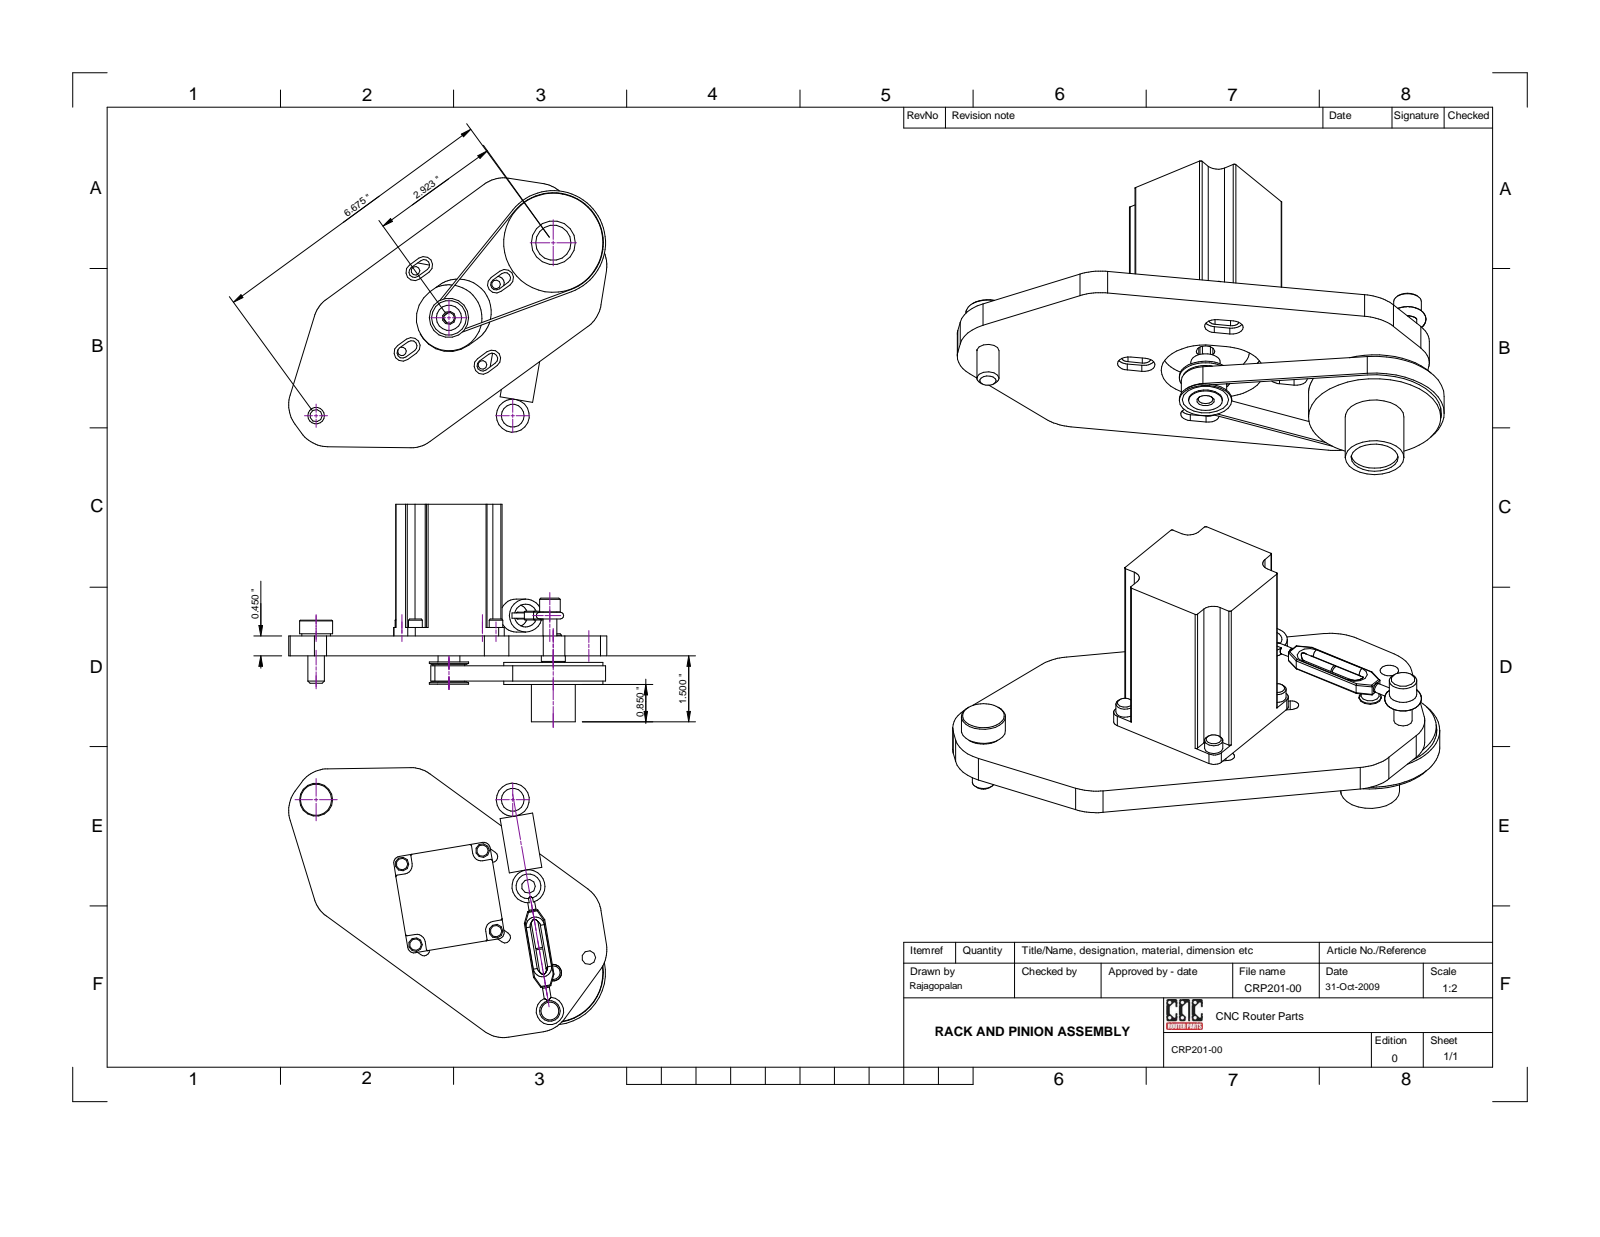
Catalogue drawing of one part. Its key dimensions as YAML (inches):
part_name: "CRP201-02 GEAR; socket head cap screw_am_B18.3.1M - 8 x 1.25 x 100 Hex SHCS -- 28NHX; CRP330-00; ISO 10423 (+8 more)"
step_written_by: "SolidWorks 2017 (AUTOMOTIVE_DESIGN)"
units: inches
bodies: {solids: 27, faces: 601, planar: 260, cylindrical: 222, other: 119}
overall_size: [7.074, 6.562, 3.083]
volume: 15.57
surface_area: 147.3
round_holes:
  - {diameter: 0.16, count: 4}
  - {diameter: 0.094, count: 2}
  - {diameter: 0.19, count: 2}
  - {diameter: 0.197, count: 2}
  - {diameter: 0.313, count: 2}
  - {diameter: 0.331, count: 2}
  - {diameter: 0.375, count: 2}
  - {diameter: 0.5, count: 2}
  - {diameter: 0.268, count: 1}
  - {diameter: 0.323, count: 1}
  - {diameter: 0.33, count: 1}
  - {diameter: 0.335, count: 1}
round_bosses_or_shafts:
  - {diameter: 0.312, count: 4}
  - {diameter: 0.19, count: 4}
  - {diameter: 0.184, count: 4}
  - {diameter: 0.63, count: 3}
  - {diameter: 0.315, count: 2}
  - {diameter: 2.255, count: 1}
  - {diameter: 1, count: 1}
  - {diameter: 0.984, count: 1}
partial_cylinders:
  - {radius: 0.125, count: 19}
  - {radius: 0.187, count: 16}
  - {radius: 0.75, count: 12}
  - {radius: 0.063, count: 5}
  - {radius: 0.063, count: 2}
  - {radius: 0.075, count: 2}
  - {radius: 0.165, count: 2}
  - {radius: 0.394, count: 1}
face_to_face_distances: [0.45, 0.5, 0.59, 0.09, 0.54, 1.04, 3.9, 0.063, 0.05, 0.049]
hole_center_spacings: [1.312, 1.856, 0.387, 2.102, 2.625, 3.659, 7.164, 0.492]
